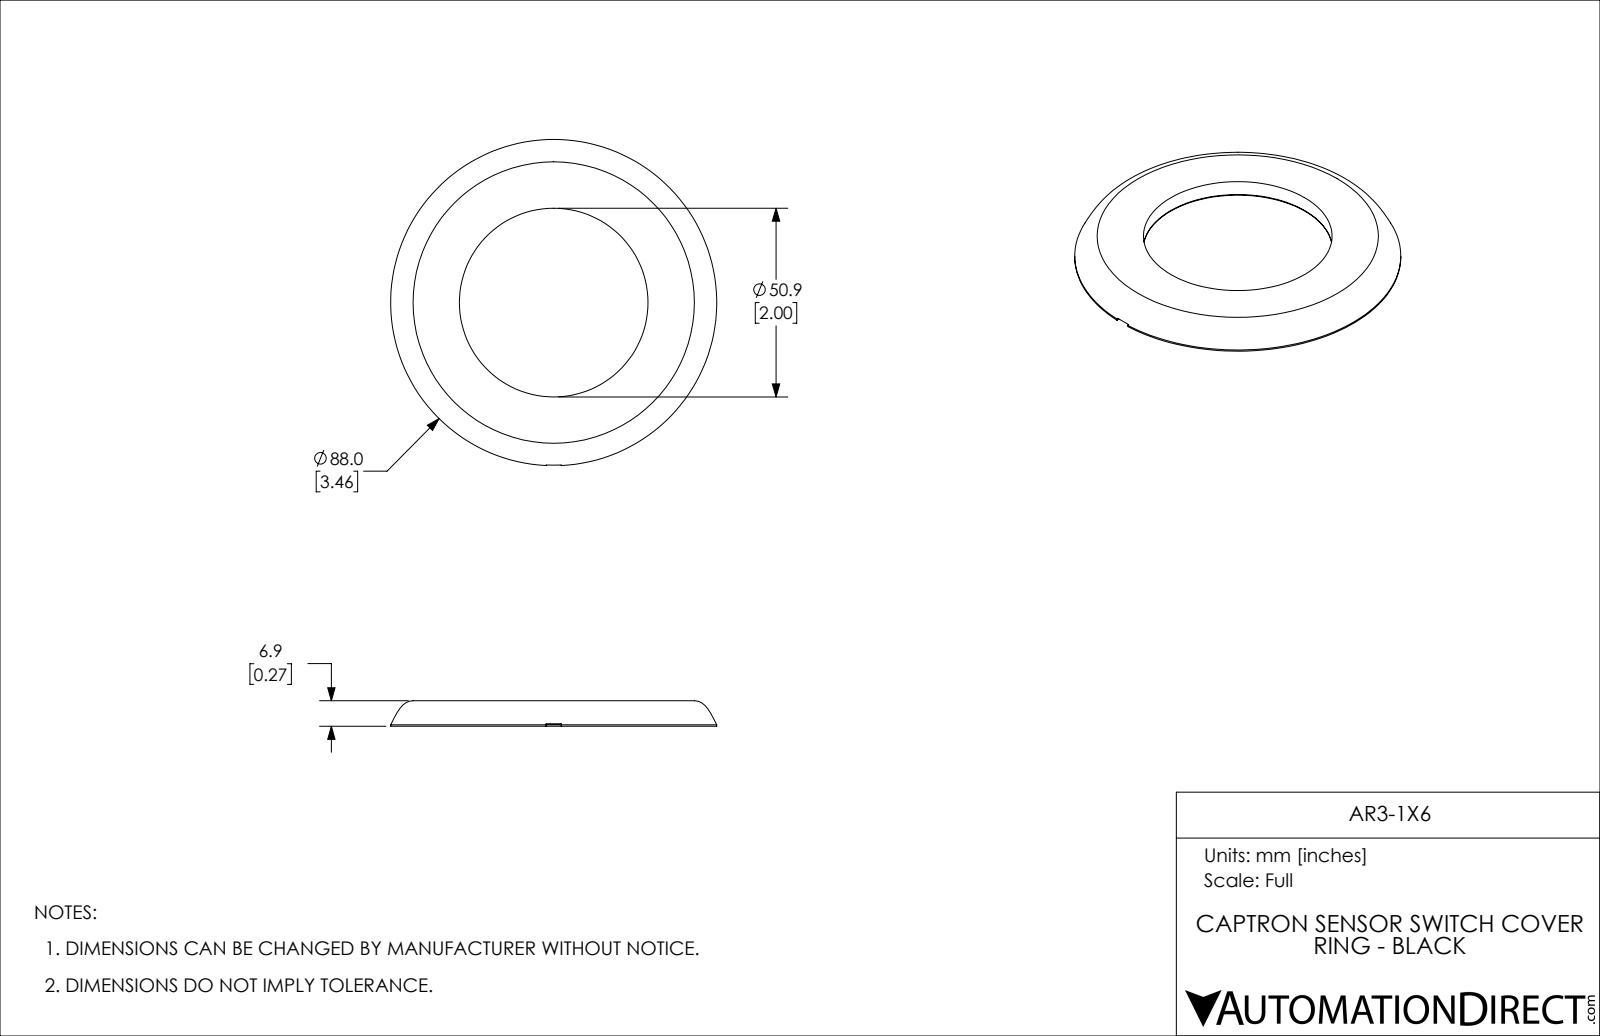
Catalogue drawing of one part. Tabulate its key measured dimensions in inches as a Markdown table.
| quantity | value |
| --- | --- |
| part name | AR3-1X6 |
| STEP written by | SolidWorks 2019 (CONFIG_CONTROL_DESIGN) |
| units | inches |
| bodies | 1 solid, 54 faces (12 planar, 4 cylindrical, 38 other) |
| overall size | 3.465 × 3.463 × 0.272 |
| volume | 0.52 in³ |
| surface area | 17.43 in² |
| round holes (diameter × count) | 0.197 × 1 |
| round bosses / shafts (diameter × count) | 2.177 × 1 |
| main face-to-face distances | 0.063, 0.122, 0.185, 0.114, 0.177, 0.118, 0.11, 0.067, 0.071, 0.079 |
